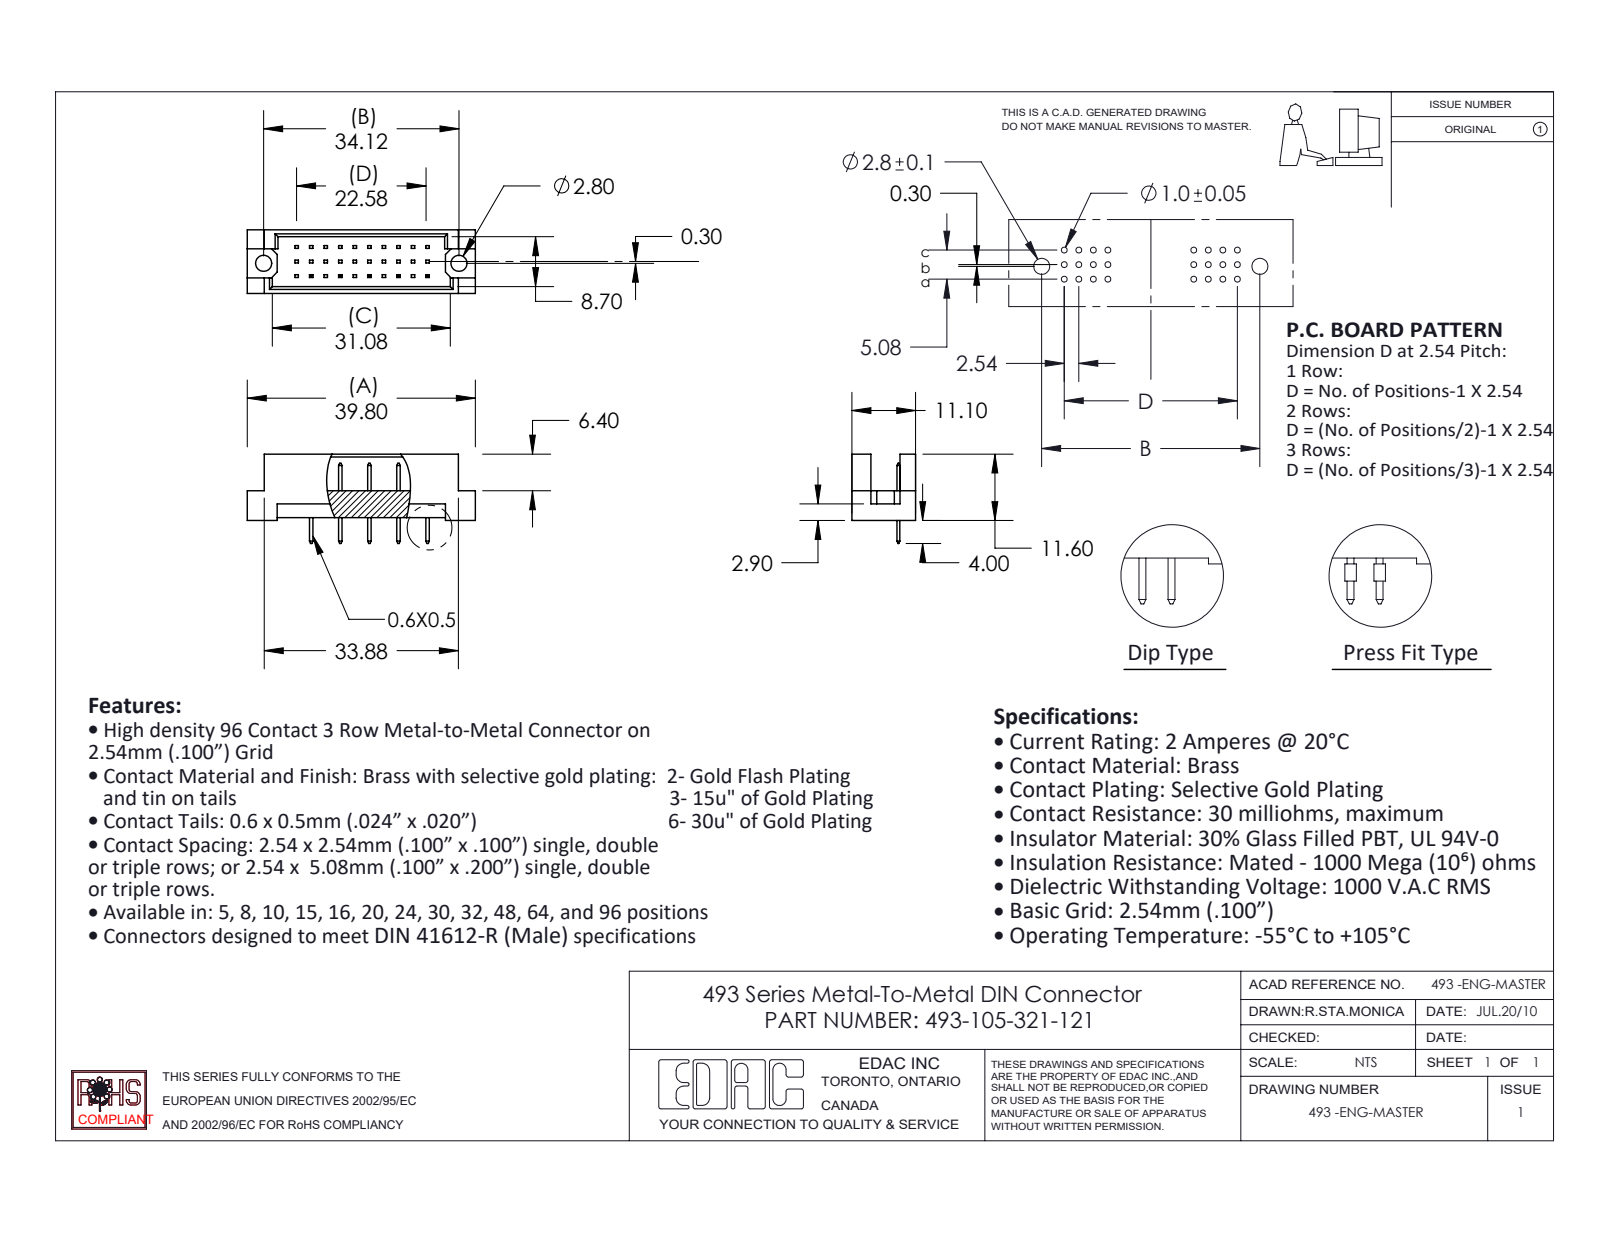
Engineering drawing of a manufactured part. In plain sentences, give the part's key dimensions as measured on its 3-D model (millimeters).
The part is named "493-105-321-122; 493 Part_30; 493-290_21". Its 3-D file was written by "SolidWorks 2020 (CONFIG_CONTROL_DESIGN)". It is 6 solids with 242 faces: 238 planar, 4 cylindrical and 0 other. Overall it measures 39.8 by 15.6 by 11.1 millimeters. Its volume is 2 394 cubic millimeters and its surface area 2 890 square millimeters. Round holes: 2 of diameter 2.8. The main face-to-face distances are 1.2, 9.9, 11.1, 8.7, 4.7, 0.5, 5.08, 2.4, 2.54, 2.3. The hole center spacings are 34.12.
